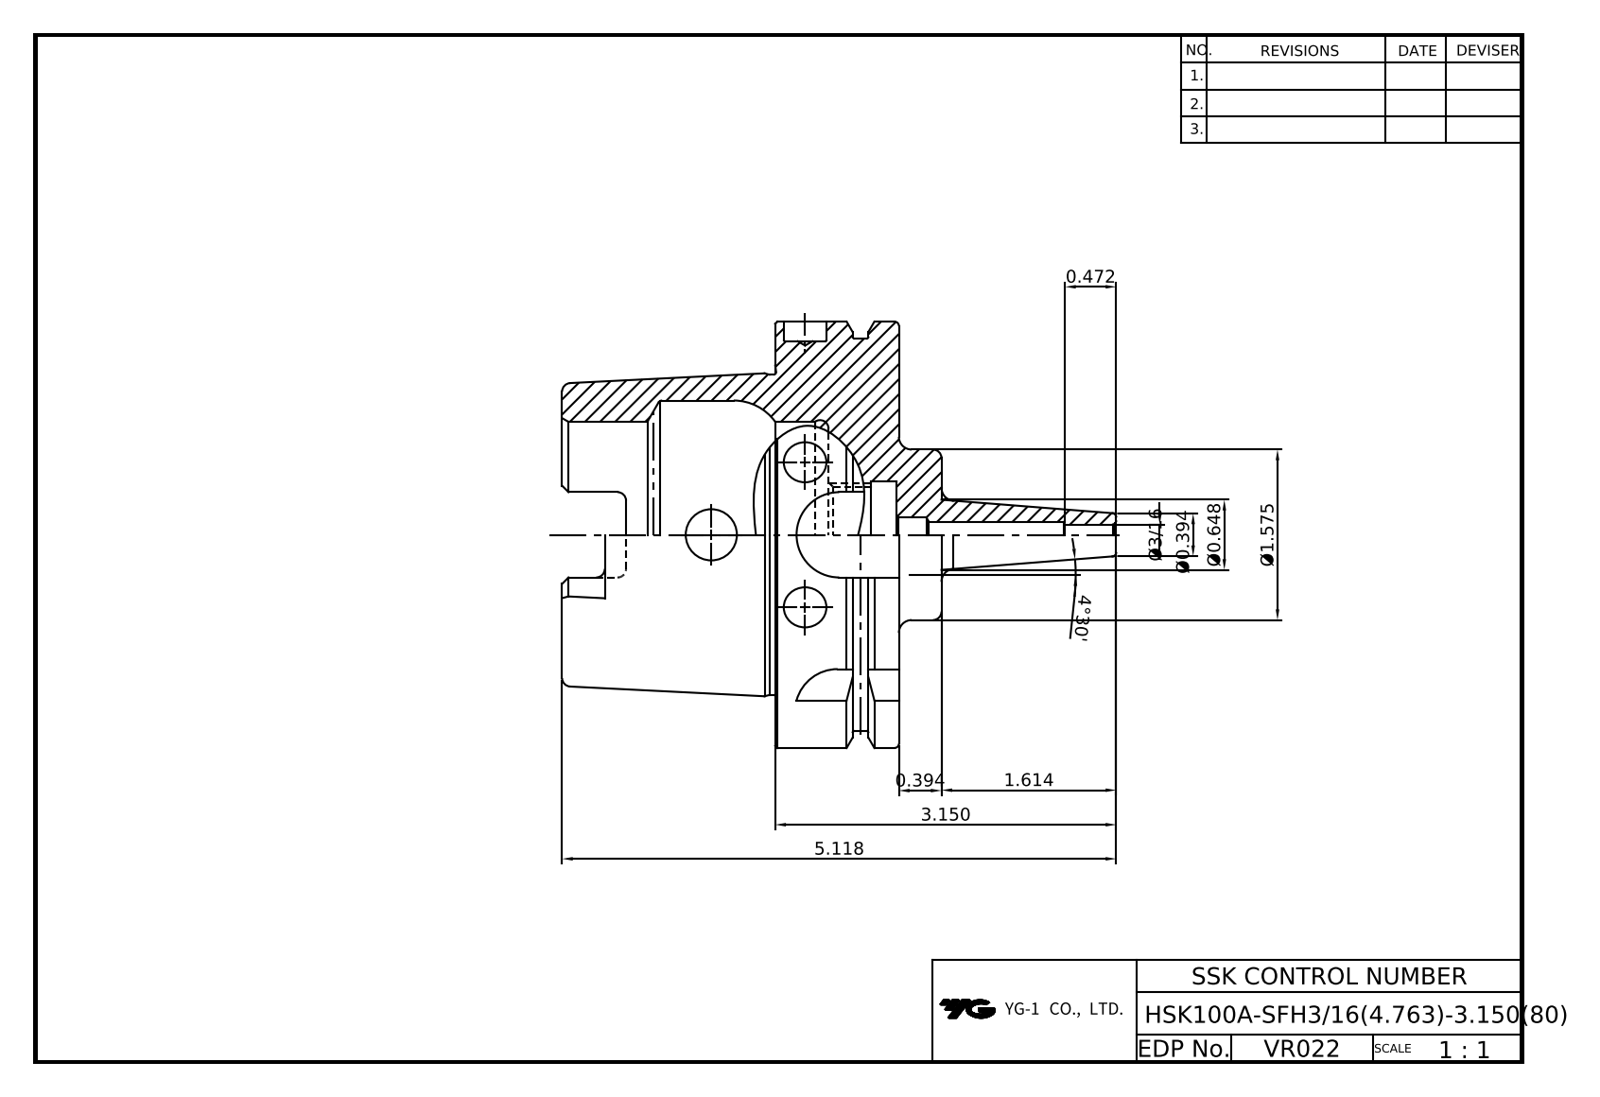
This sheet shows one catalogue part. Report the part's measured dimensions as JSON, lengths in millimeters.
{"part_name": "LO-HSK100A-SFH4.7625-3.15", "step_written_by": "Autodesk Inventor 2022 (AUTOMOTIVE_DESIGN)", "units": "millimeters", "bodies": {"solids": 1, "faces": 120, "planar": 37, "cylindrical": 36, "other": 47}, "overall_size": [130, 100, 100], "volume_mm3": 270759, "surface_area_mm2": 53258, "round_holes": [[10, 3], [4.76, 1], [6, 1], [8, 1], [12, 1], [22.38, 1], [25, 1], [53, 1], [63, 1]], "round_bosses_or_shafts": [[100, 1], [92, 1], [75.41, 1], [40, 1]], "partial_cylinders_radius": [[2, 6], [4.88, 4], [10, 4]], "face_to_face_distances": [29, 12.5, 16.5, 79, 62.5, 10, 50, 89, 39, 26.5]}
